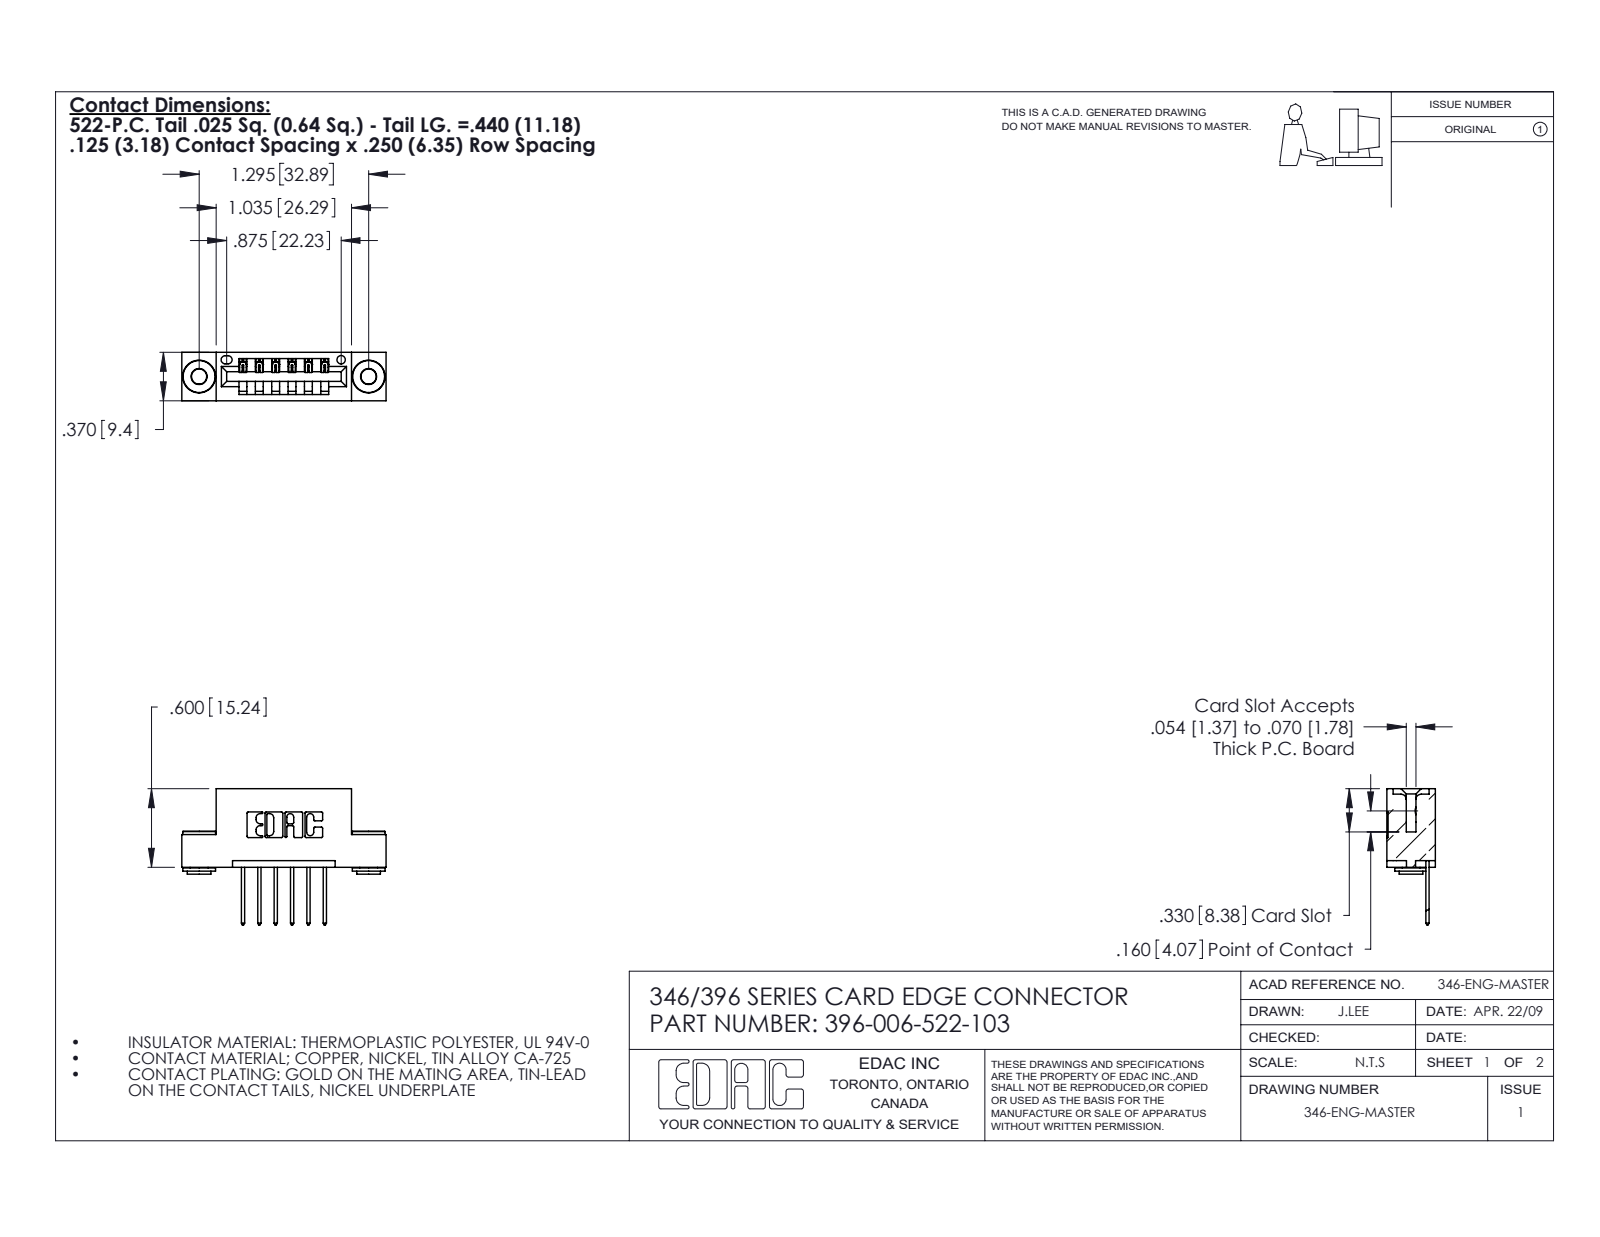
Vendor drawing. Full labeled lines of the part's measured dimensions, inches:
Part name (STEP PRODUCT): 345-292-001_345-293-122; 396-006-522-103; 346 Part_Flush Mounting Lugs - 0.156 Dia-TH; 345-250-002_345-250-002-102
STEP written by: SolidWorks 2020 (CONFIG_CONTROL_DESIGN)
Units: inches
Bodies: 9 solids, 522 faces (340 planar, 174 cylindrical, 8 other)
Overall size (bounding box): 1.56 × 1.04 × 0.37
Volume: 0.216 in³ · Surface area: 6.693 in²
Round holes (diameter × count): ⌀0.116 ×2, ⌀0.156 ×2, ⌀0.064 ×1
Round bosses / shafts (diameter × count): ⌀0.25 ×2, ⌀0.18 ×2, ⌀0.136 ×2
Partial cylindrical surfaces — rounded edges, fillets, slot ends (radius × count): R0.01 ×22, R0.006 ×12, R0.01 ×12, R0.007 ×6, R0.031 ×6, R0.026 ×3, R0.031 ×2, R0.04 ×2
Main face-to-face distances: 0.25, 0.37, 0.048, 0.322, 0.025, 0.148, 0.072, 0.298, 0.222, 0.1
Hole centre spacings: 0.246, 1.092, 1.295
